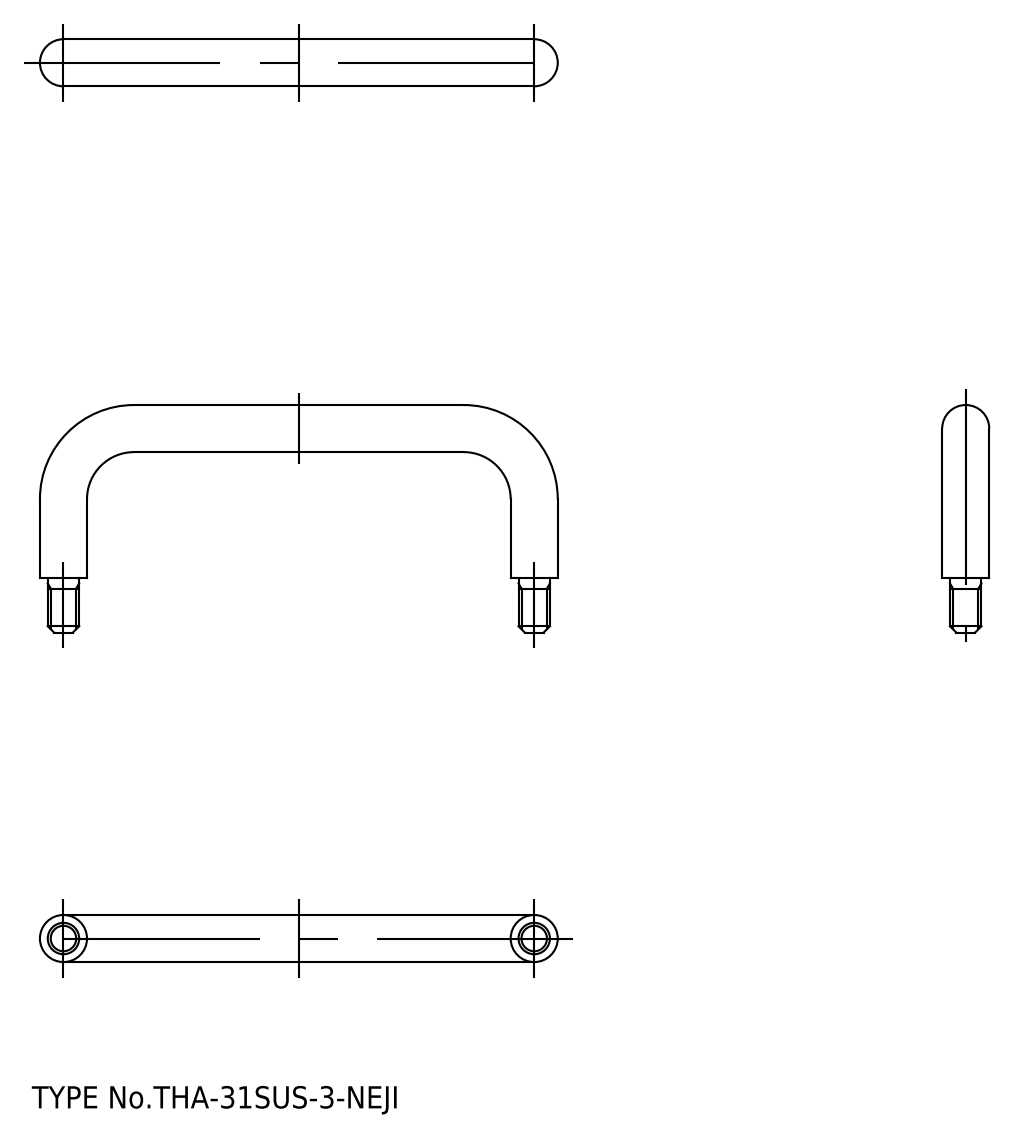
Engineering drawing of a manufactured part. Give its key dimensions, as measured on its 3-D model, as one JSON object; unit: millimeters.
{"step_written_by": "spGate 17.5.2 (AUTOMOTIVE_DESIGN)", "units": "millimeters", "bodies": {"solids": 1, "faces": 22, "planar": 4, "cylindrical": 10, "other": 8}, "overall_size": [66, 29, 6], "volume_mm3": 2727, "surface_area_mm2": 1929, "round_bosses_or_shafts": [[6, 3], [4.01, 2]], "face_to_face_distances": [7]}
